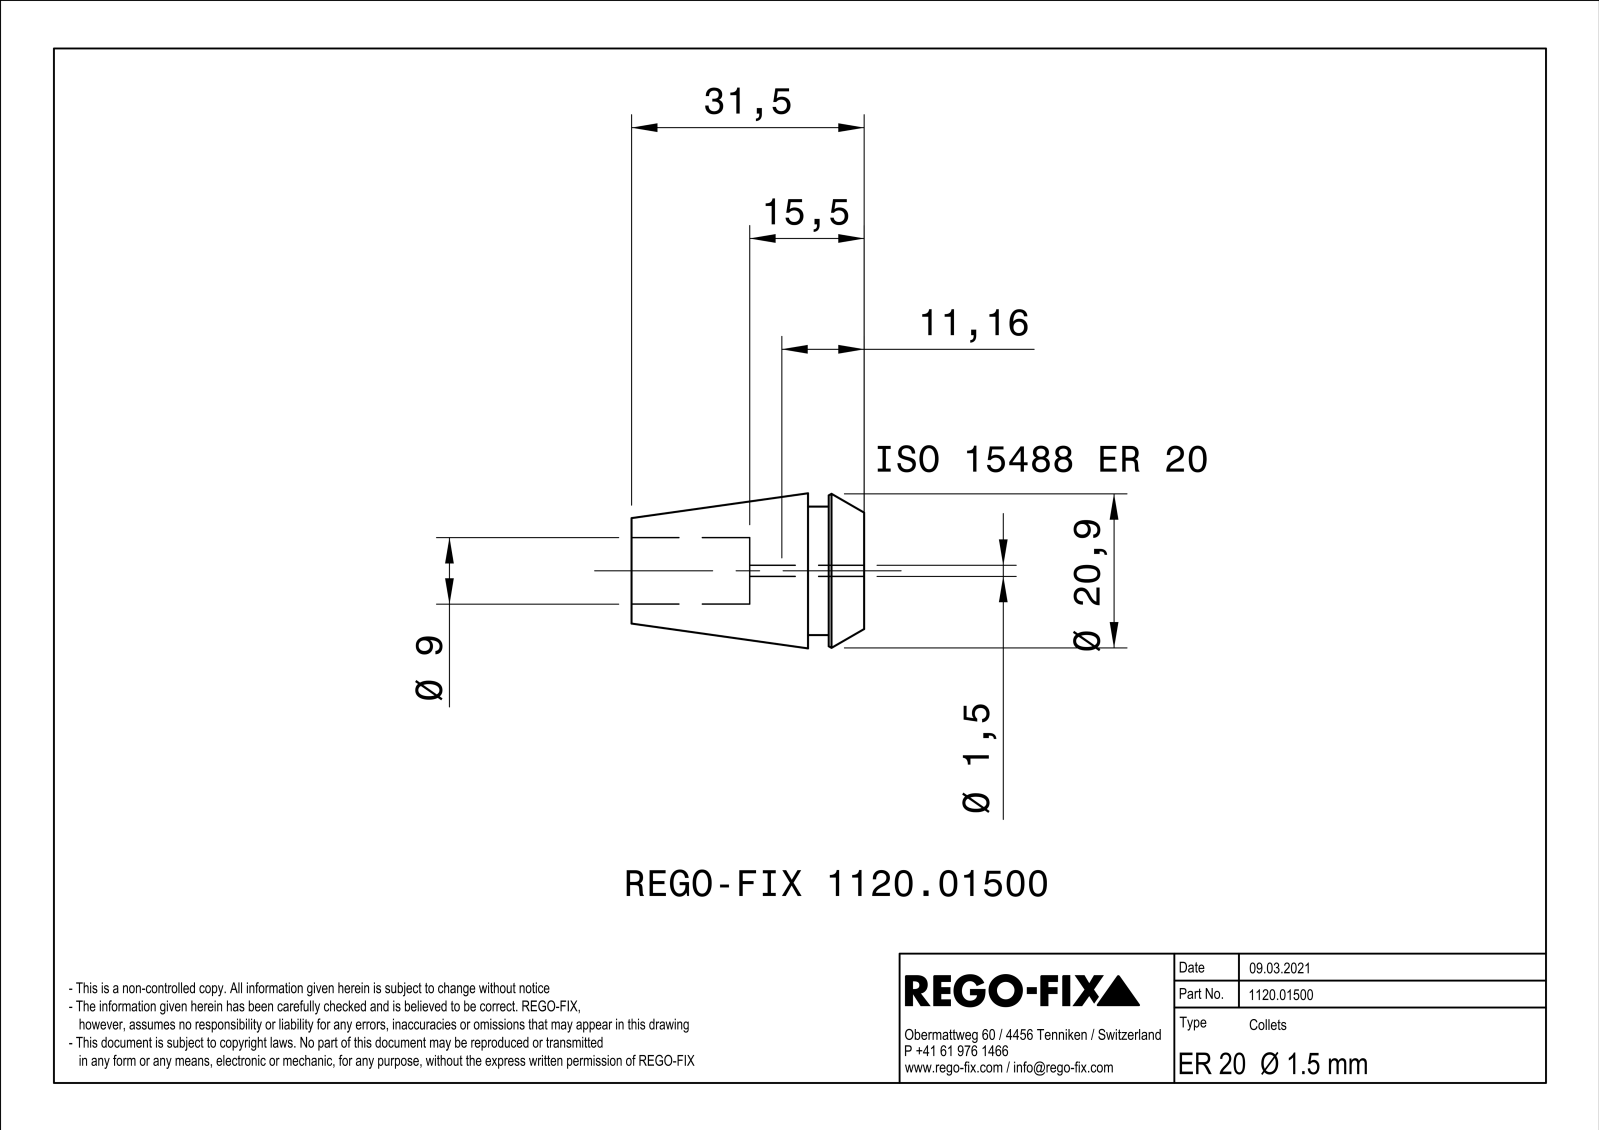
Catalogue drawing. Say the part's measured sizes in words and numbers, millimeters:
The part is named "NOCUT". Its 3-D file was written by "SIEMENS PLM Software Solid Edge ST10 (AUTOMOTIVE_DESIGN)". It is 1 solid with 245 faces: 100 planar, 41 cylindrical and 104 other. Overall it measures 31.5 by 21 by 21 millimeters. Its volume is 5 877 cubic millimeters and its surface area 6 770 square millimeters. Round holes: 1 of diameter 9. Round bosses or shafts: 1 of diameter 17.4. Partial cylindrical surfaces (rounded edges, fillets, slot ends): 8 of radius 35, 1 of radius 0.75. The main face-to-face distances are 0.45, 0.44, 0.46, 7.6, 4.8, 2.8, 31.5, 26.7, 23.9, 15.5.
